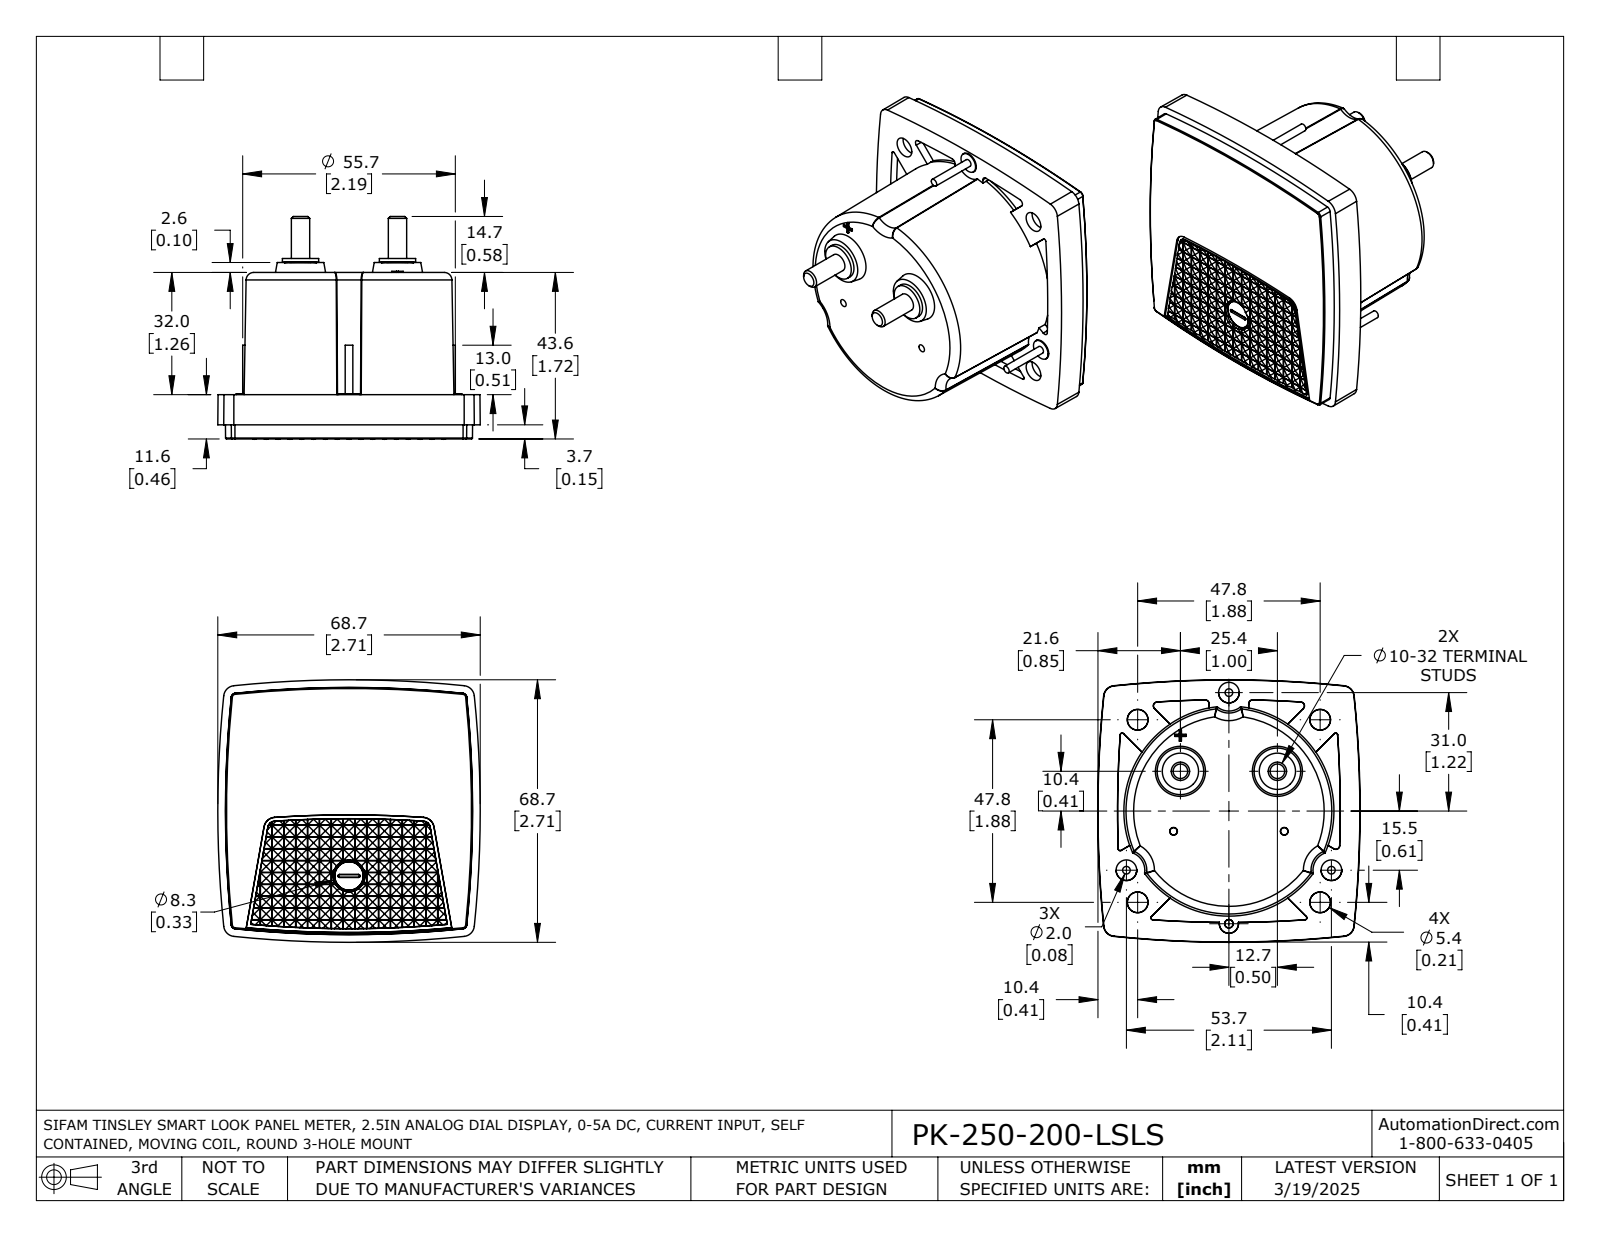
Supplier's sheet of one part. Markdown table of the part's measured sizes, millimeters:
| quantity | value |
| --- | --- |
| part name | PK-250-200-LSLS |
| STEP written by | SolidWorks 2021 (AUTOMOTIVE_DESIGN) |
| units | millimeters |
| bodies | 1 solid, 1550 faces (1165 planar, 265 cylindrical, 120 other) |
| overall size | 68.7 × 68.7 × 58.3 |
| volume | 124 400 mm³ |
| surface area | 19 620 mm² |
| round bosses / shafts (diameter × count) | 5.4 × 3, 2 × 3, 9.5 × 2, 4.8 × 2, 5.5 × 1 |
| partial cylindrical surfaces (radius × count) | 4.2 × 2, 27.5 × 1 |
| main face-to-face distances | 43.6, 32, 11.6, 0.6, 2.2, 2.4, 7.9, 3, 1.8, 34.2 |
